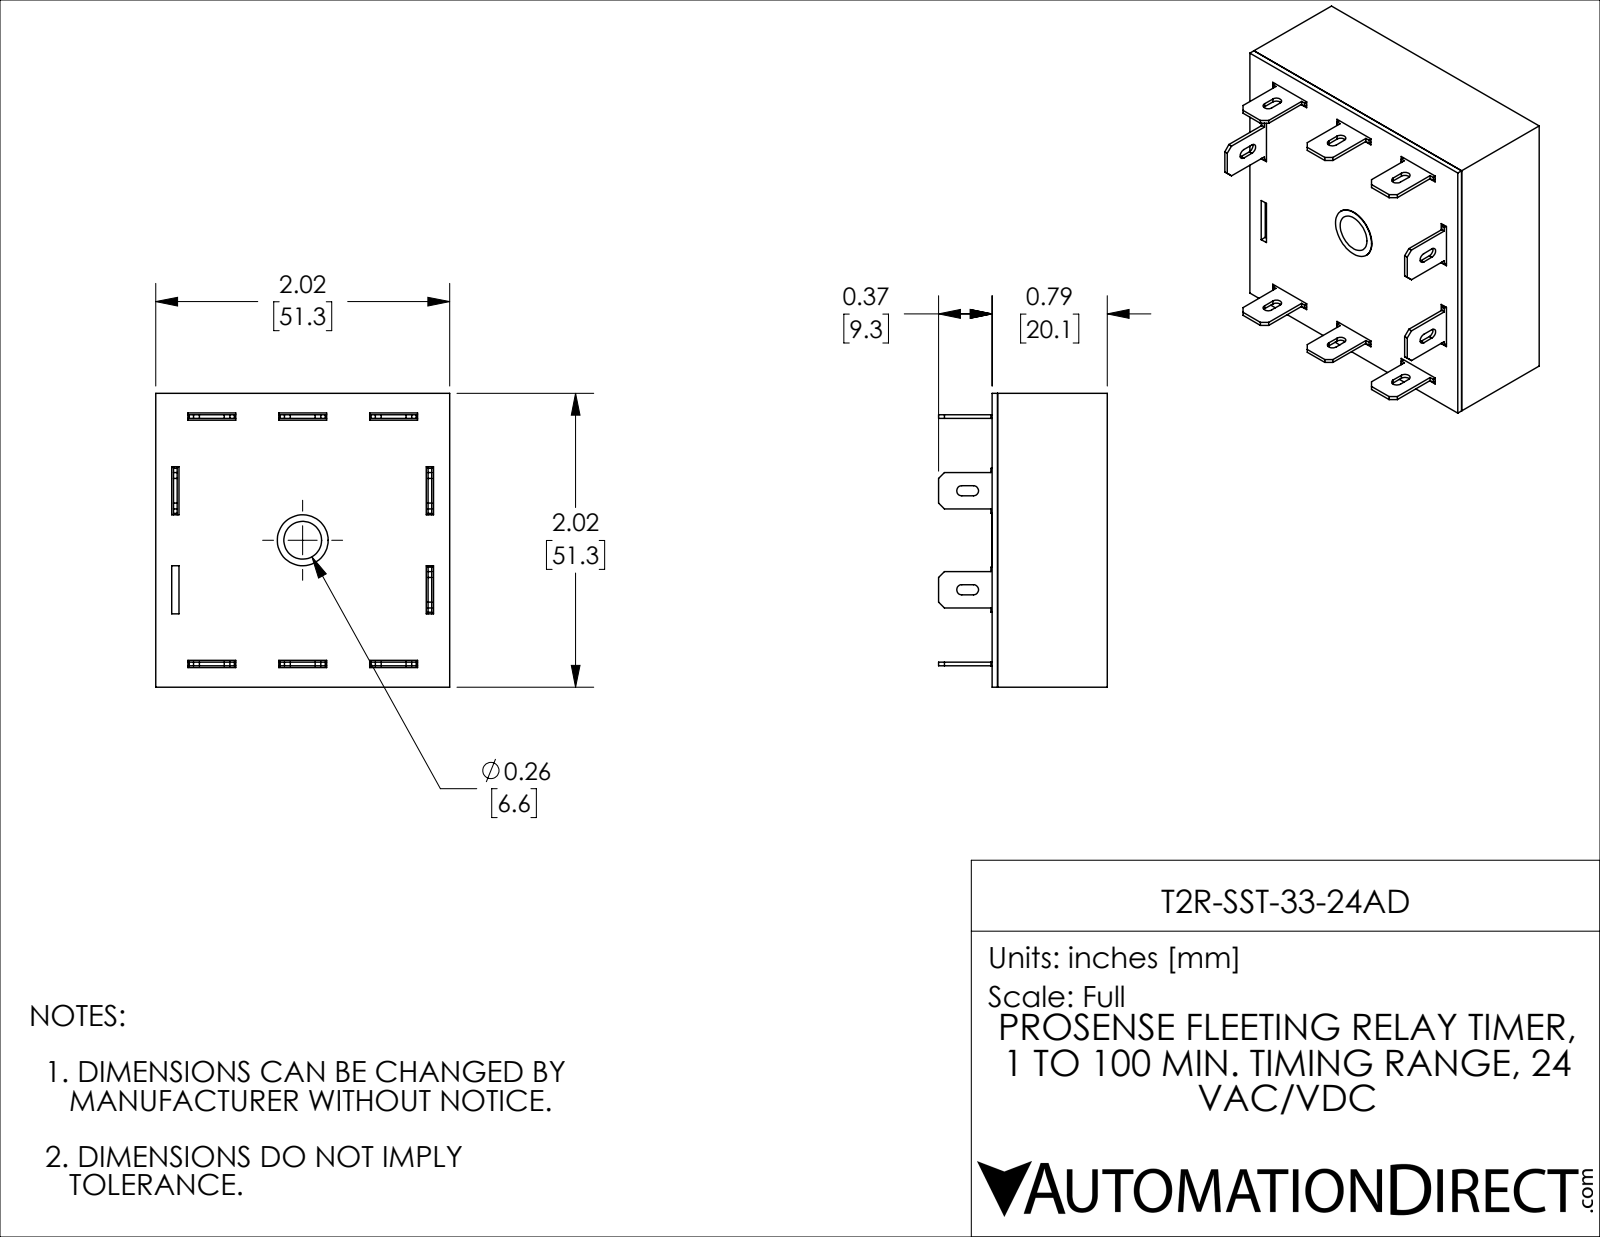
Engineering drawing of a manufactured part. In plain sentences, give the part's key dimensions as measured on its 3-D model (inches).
The part is named "T2R-SST-33-24AD". Its 3-D file was written by "SolidWorks 2021 (CONFIG_CONTROL_DESIGN)". It is 11 solids with 280 faces: 256 planar, 22 cylindrical and 2 other. Overall it measures 2.02 by 2.02 by 1.16 inches. Its volume is 0.682 cubic inches and its surface area 36.12 square inches. Round holes: 1 of diameter 0.35. Partial cylindrical surfaces (rounded edges, fillets, slot ends): 10 of radius 0.035. The main face-to-face distances are 0.045, 1.975, 0.754, 0.792, 0.038, 0.709, 0.747, 2.02, 0.147, 1.872.
